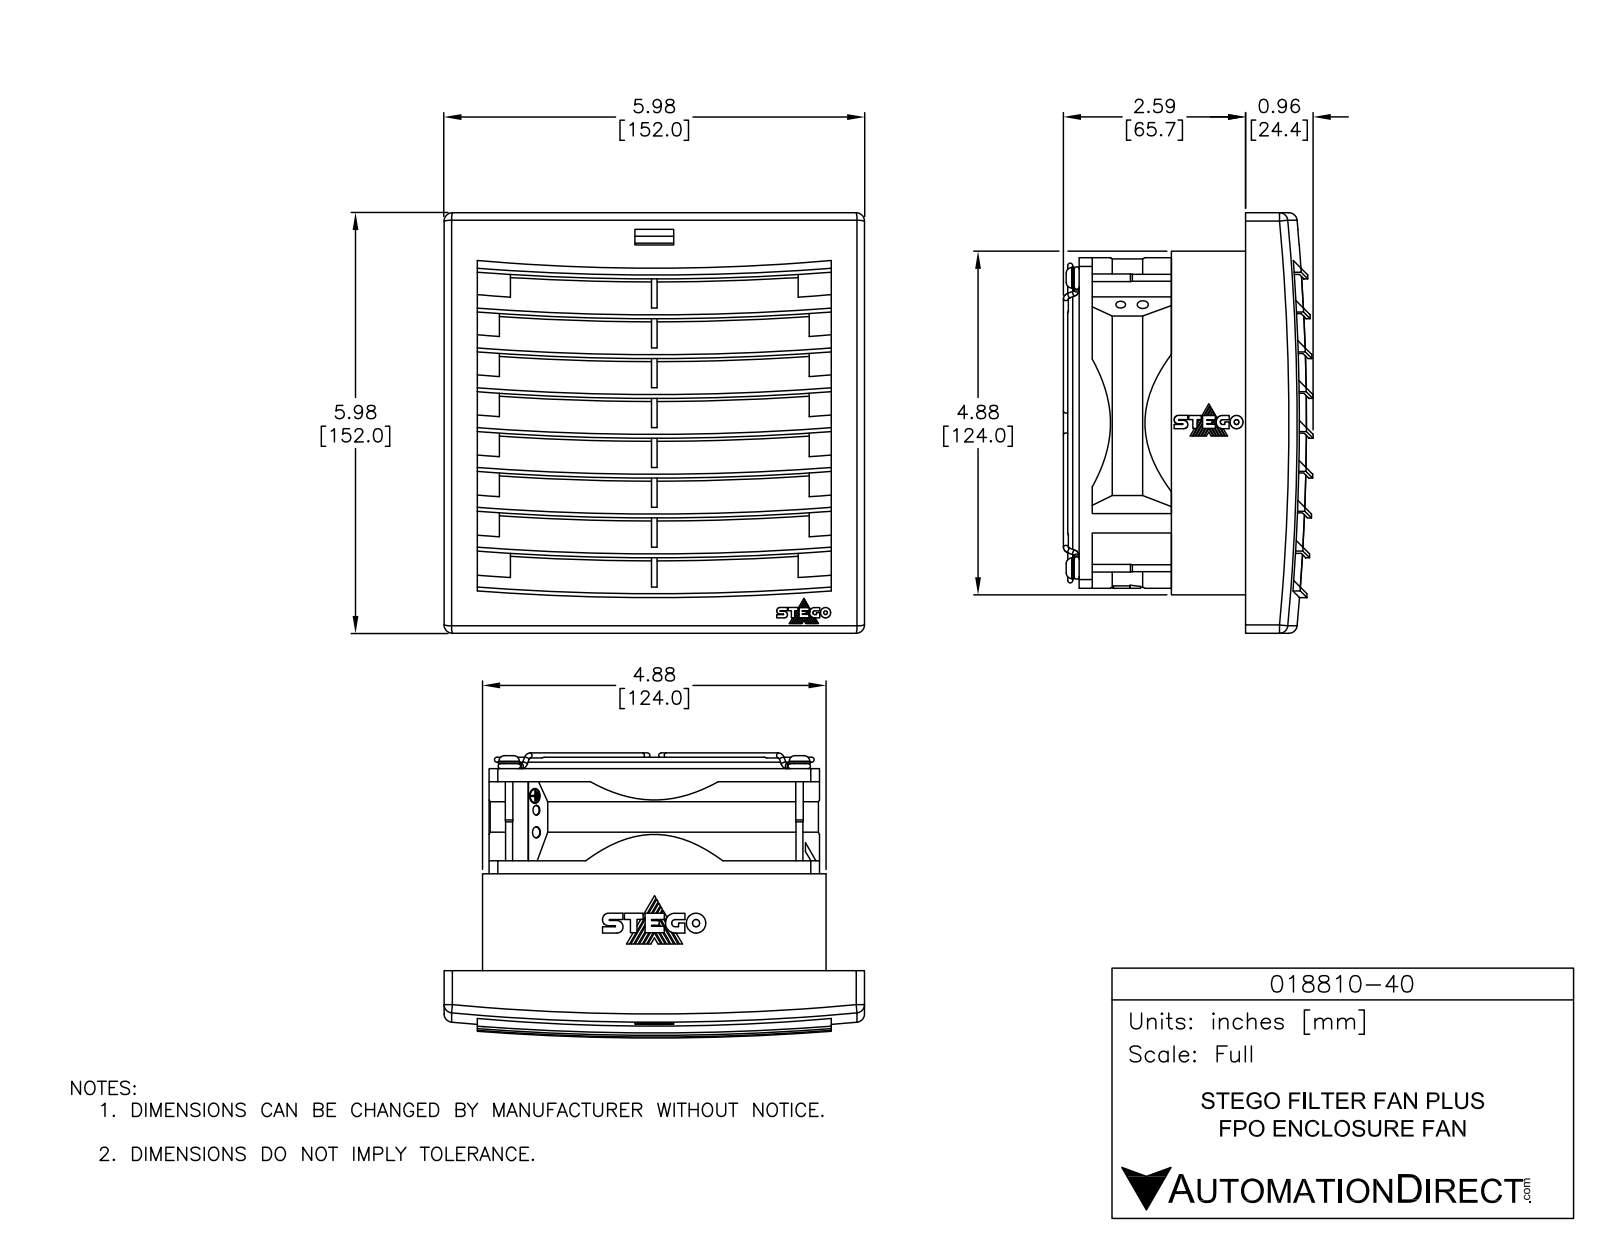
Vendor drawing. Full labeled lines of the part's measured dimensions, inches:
Part name (STEP PRODUCT): 018810-40
STEP written by: SolidWorks 2018 (AUTOMOTIVE_DESIGN)
Units: inches
Bodies: 1 solid, 520 faces (305 planar, 207 cylindrical, 8 other)
Overall size (bounding box): 5.985 × 5.984 × 4.094
Volume: 31.5 in³ · Surface area: 314.4 in²
Round holes (diameter × count): ⌀0.256 ×4, ⌀0.98 ×1, ⌀1.66 ×1, ⌀2.34 ×1, ⌀3.02 ×1, ⌀3.253 ×1, ⌀3.78 ×1, ⌀4.15 ×1
Round bosses / shafts (diameter × count): ⌀4.346 ×1, ⌀3.49 ×1, ⌀3.178 ×1, ⌀2.712 ×1, ⌀2.498 ×1, ⌀1.817 ×1, ⌀1.323 ×1, ⌀1.137 ×1
Partial cylindrical surfaces — rounded edges, fillets, slot ends (radius × count): R13.757 ×16, R1.852 ×5, R0.118 ×4, R0.142 ×4, R0.519 ×1, R0.849 ×1, R0.967 ×1, R1.238 ×1
Main face-to-face distances: 0.426, 0.059, 0.122, 4.76, 0.852, 0.079, 0.485, 0.367, 4.638, 0.551
Hole centre spacings: 3.007, 4.252, 6.013
